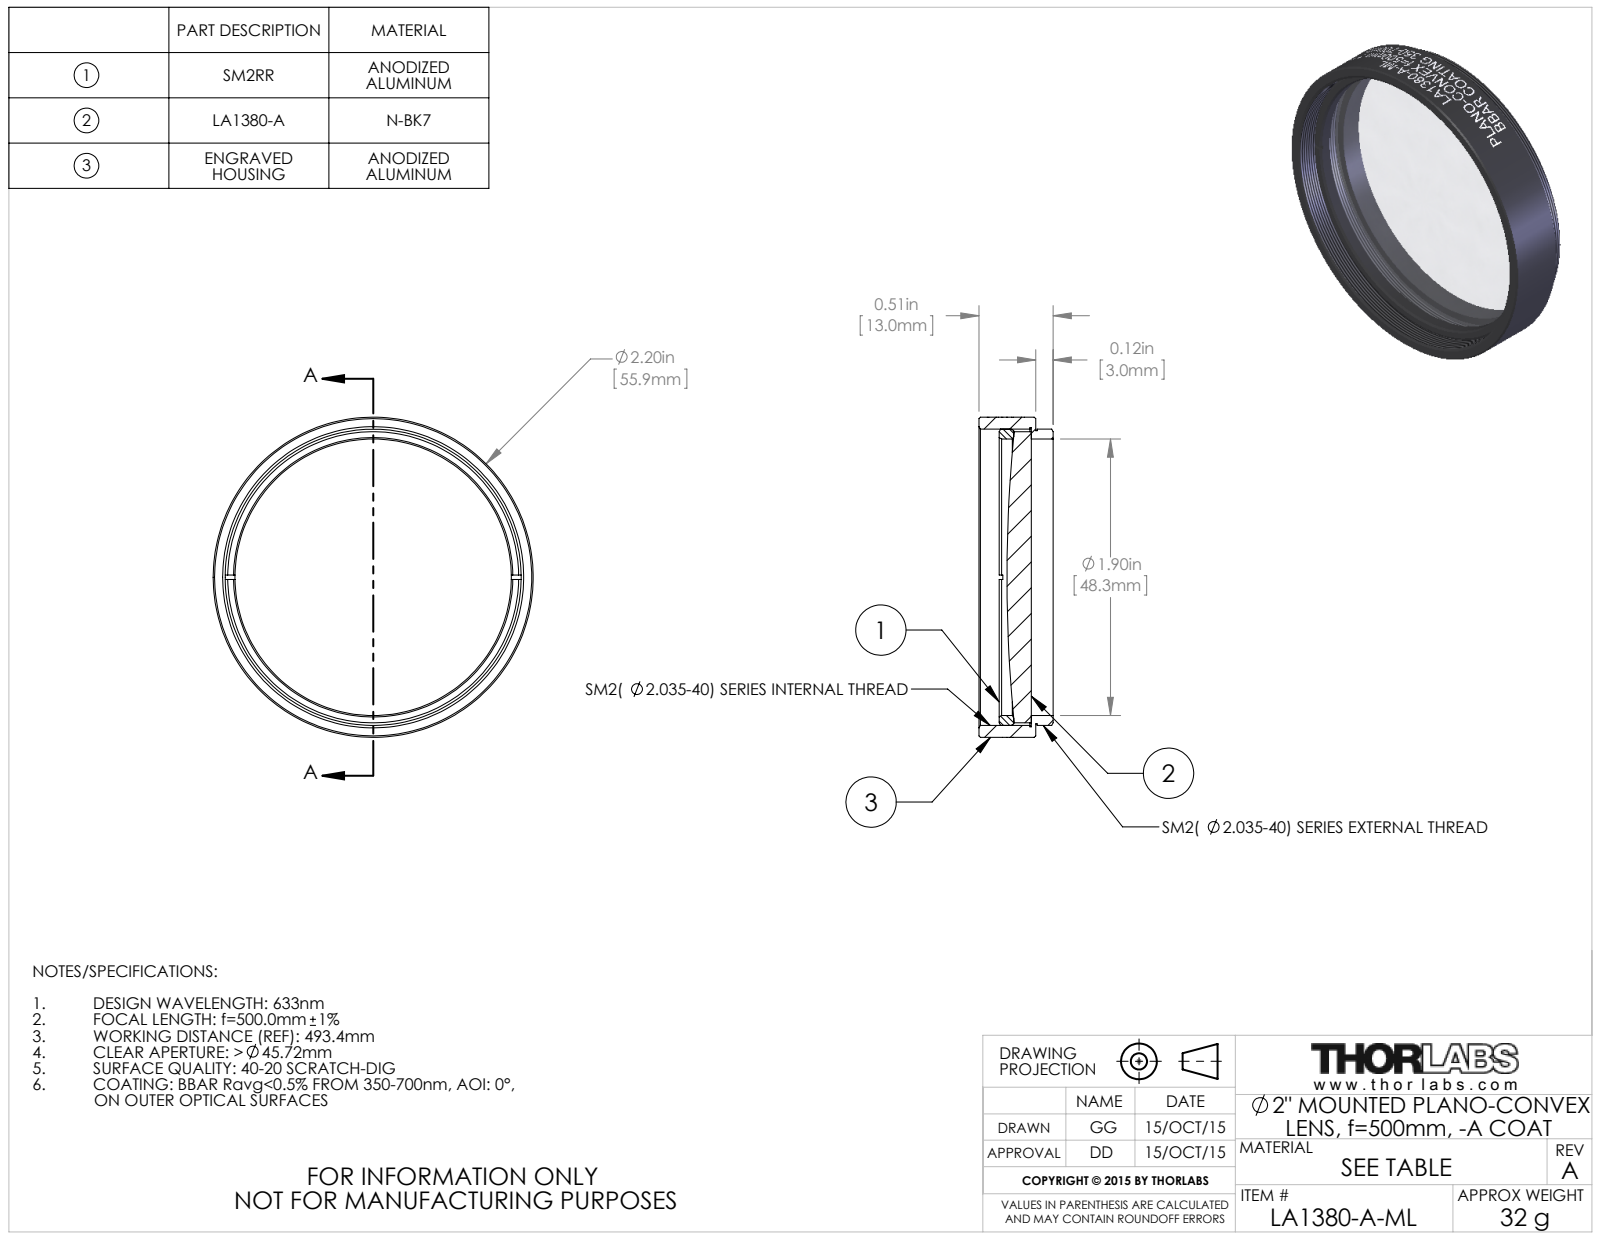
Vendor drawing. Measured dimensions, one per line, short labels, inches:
name: TTN039561-E0W
written by: SolidWorks 2014 (CONFIG_CONTROL_DESIGN)
unit: in
bodies: 3 solids, 144 faces (16 planar, 108 cylindrical, 20 other)
size: 2.2 × 2.2 × 0.51
volume: 0.761 in³; area: 17.6 in²
holes: 1× ⌀1.9, 1× ⌀2.055
bosses: 1× ⌀2.2, 1× ⌀2.035, 1× ⌀2.015, 1× ⌀2
face distances: 0.03, 0.39, 0.36, 0.12, 0.15, 0.51, 0.271, 0.151, 0.121, 0.239
